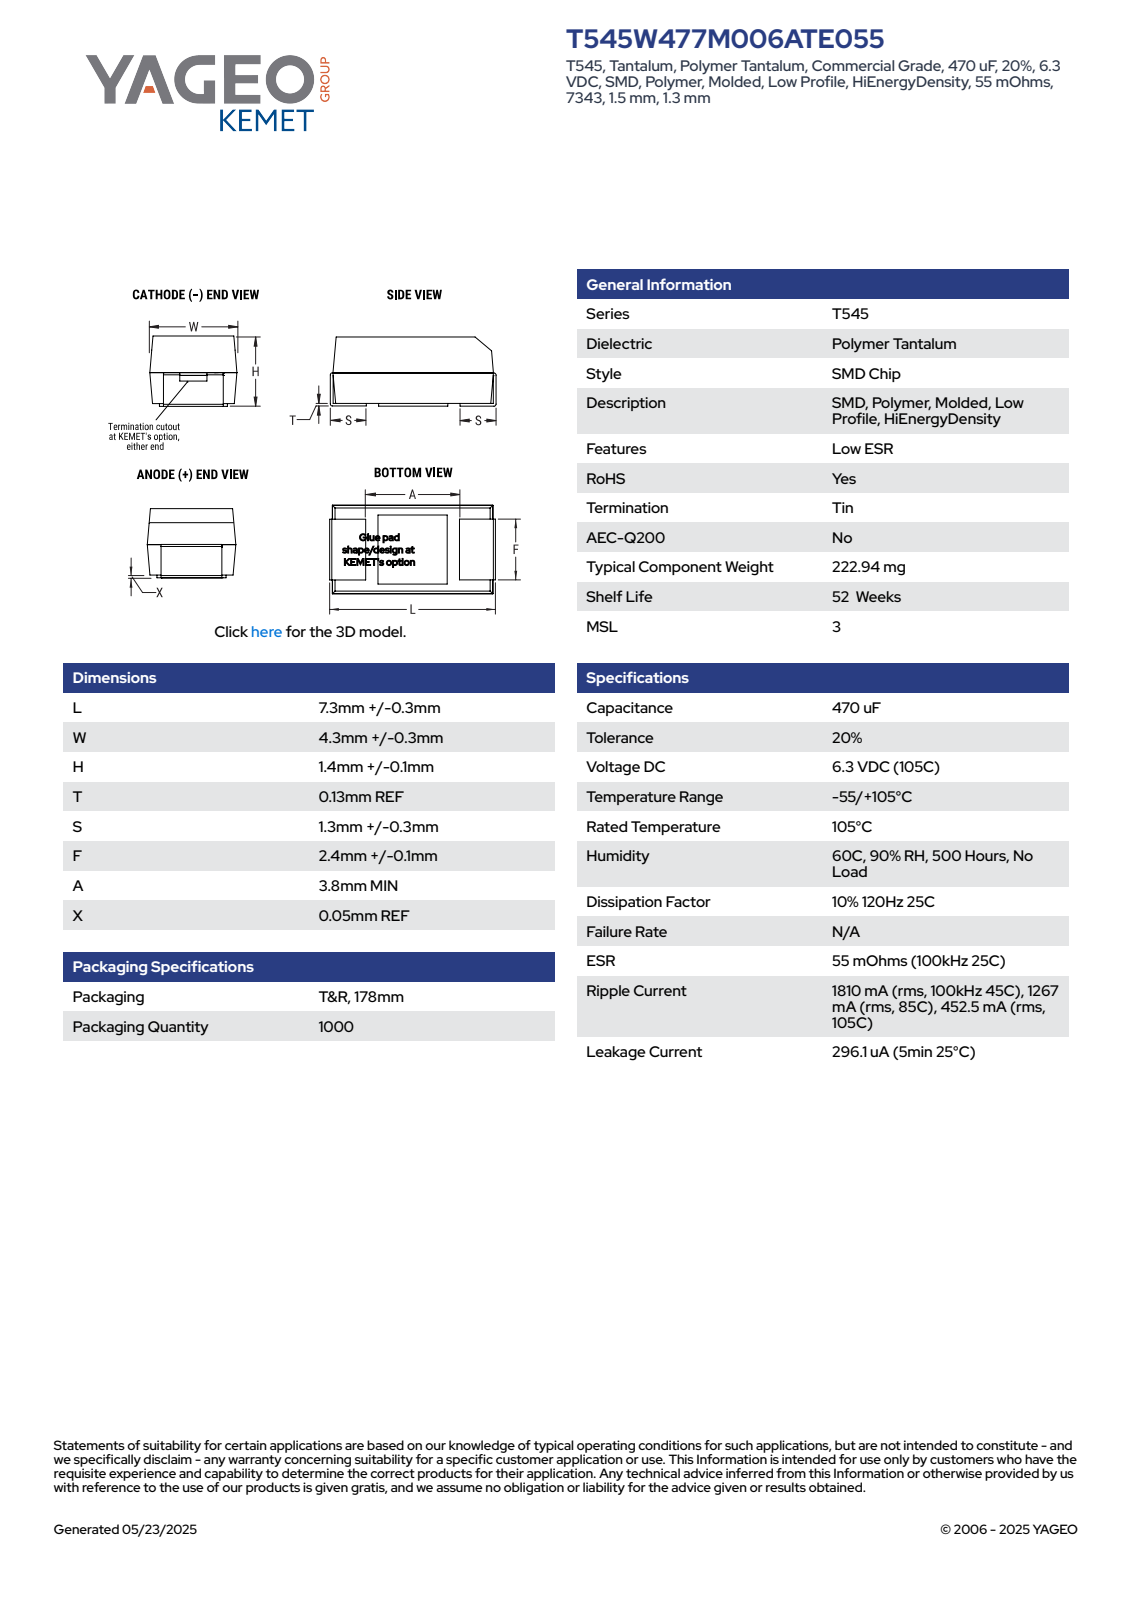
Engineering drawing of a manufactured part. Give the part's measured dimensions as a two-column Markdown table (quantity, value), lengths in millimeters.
| quantity | value |
| --- | --- |
| part name | CTSM_TCM2NBKRPEG_7343_L7.6W4.6H1.5T0.13S1.3F2.5A3.8X0.05 |
| STEP written by | SolidWorks 2014 (AUTOMOTIVE_DESIGN) |
| units | millimeters |
| bodies | 4 solids, 90 faces (86 planar, 4 cylindrical, 0 other) |
| overall size | 7.6 × 4.6 × 1.64 |
| volume | 47 mm³ |
| surface area | 104 mm² |
| partial cylindrical surfaces (radius × count) | 0.1 × 4 |
| main face-to-face distances | 1.5, 4.34, 1.63, 7.47, 7.6, 7.34, 1.3, 6.3, 1.17, 6.17 |
